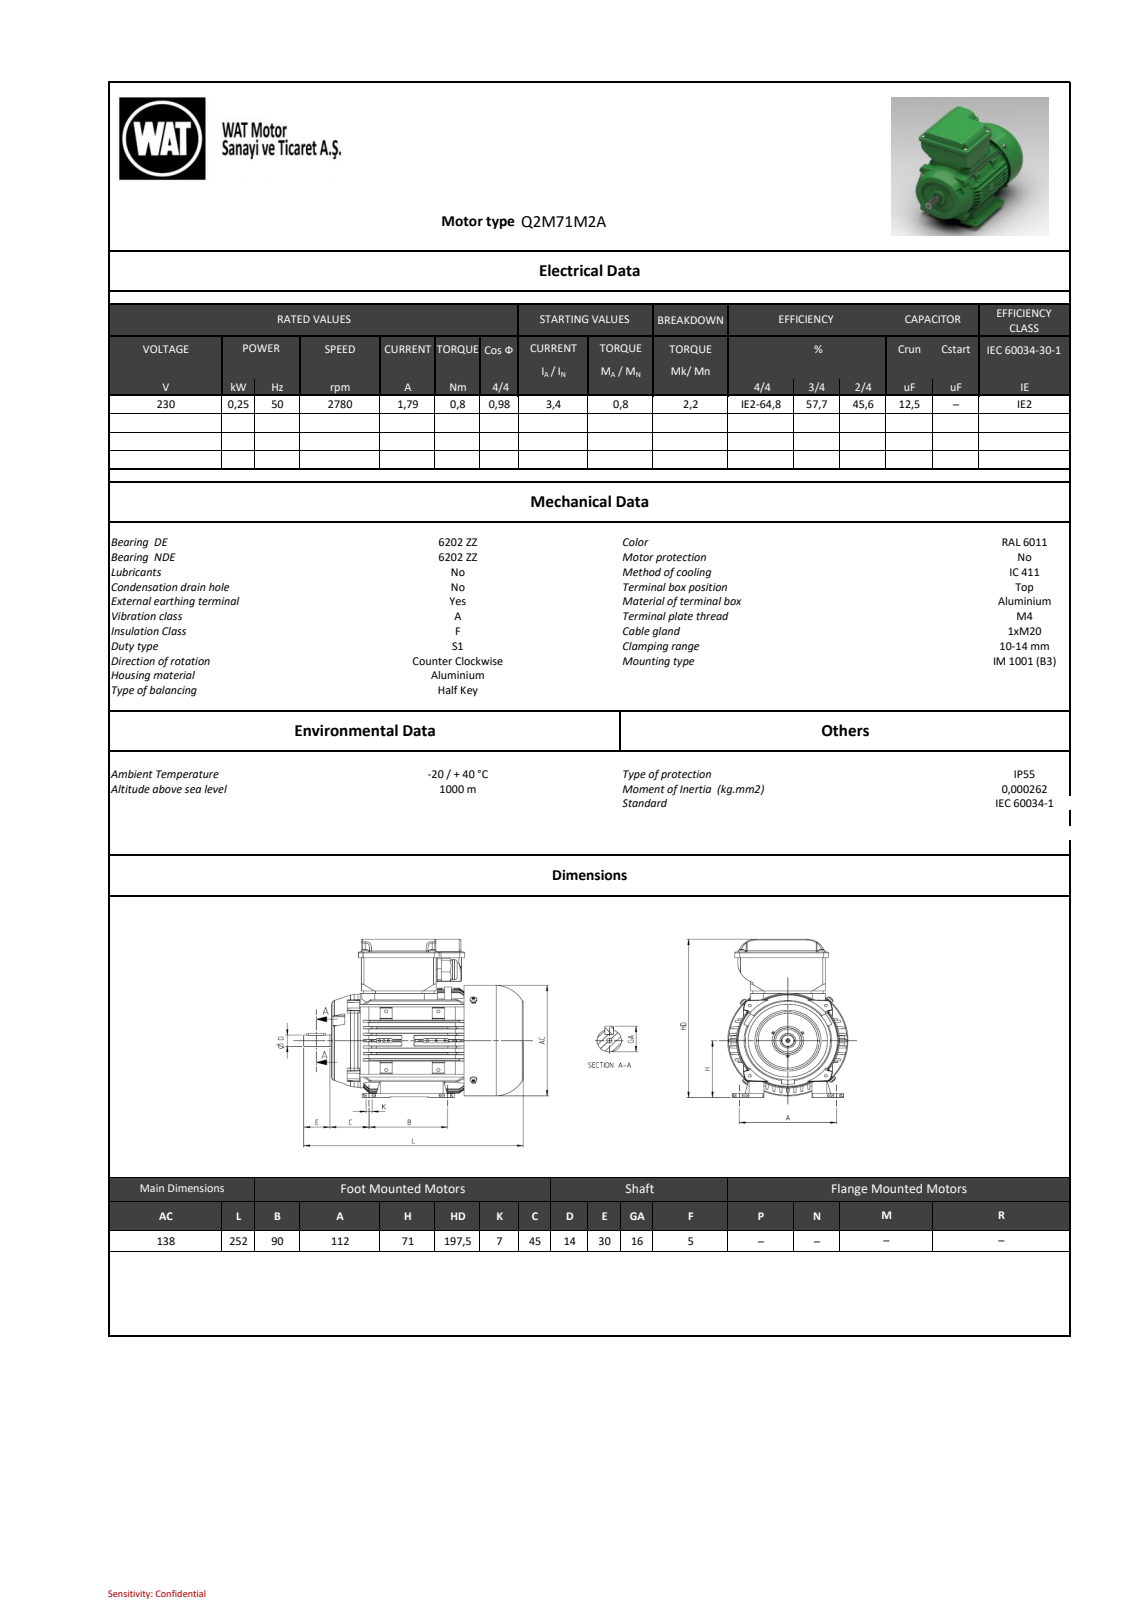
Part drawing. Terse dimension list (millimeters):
name: BY6434017xx_004-TK_QM63-80; BY6424130xx_004-TKK_QM63-80; 641304741_AZ-KAMA PARALEL A 5x5x22 St50 DIN6885; BY6424098xx_006-AYAK_QS71_SOL_83826ID (+8 more)
written by: SIEMENS PLM Software NX2206.8101 (AUTOMOTIVE_DESIGN)
unit: mm
bodies: 26 solids, 2645 faces (1307 planar, 727 cylindrical, 611 other)
size: 252 × 197.5 × 138
volume: 747 491 mm³; area: 484 127 mm²
holes: 13× ⌀3.3, 8× ⌀3.65, 8× ⌀4.5, 6× ⌀2.5, 4× ⌀4.65, 4× ⌀4.8, 4× ⌀5.2, 4× ⌀7, 3× ⌀3, 3× ⌀3.7, 2× ⌀4.6, 1× ⌀5
bosses: 8× ⌀8, 8× ⌀4, 8× ⌀3, 1× ⌀138, 1× ⌀136, 1× ⌀116, 1× ⌀115, 1× ⌀77
rounds: 117× R1, 50× R2, 38× R0.5, 36× R1.2, 20× R2.5, 13× R5.5, 12× R0.3, 12× R1.5
face distances: 3, 146.5, 4, 177.5, 67.5, 1, 174.5, 3.5, 31, 180.5
hole spacings: 55, 36.59, 60, 28.5, 37.26, 61.87, 66.91, 68.11
